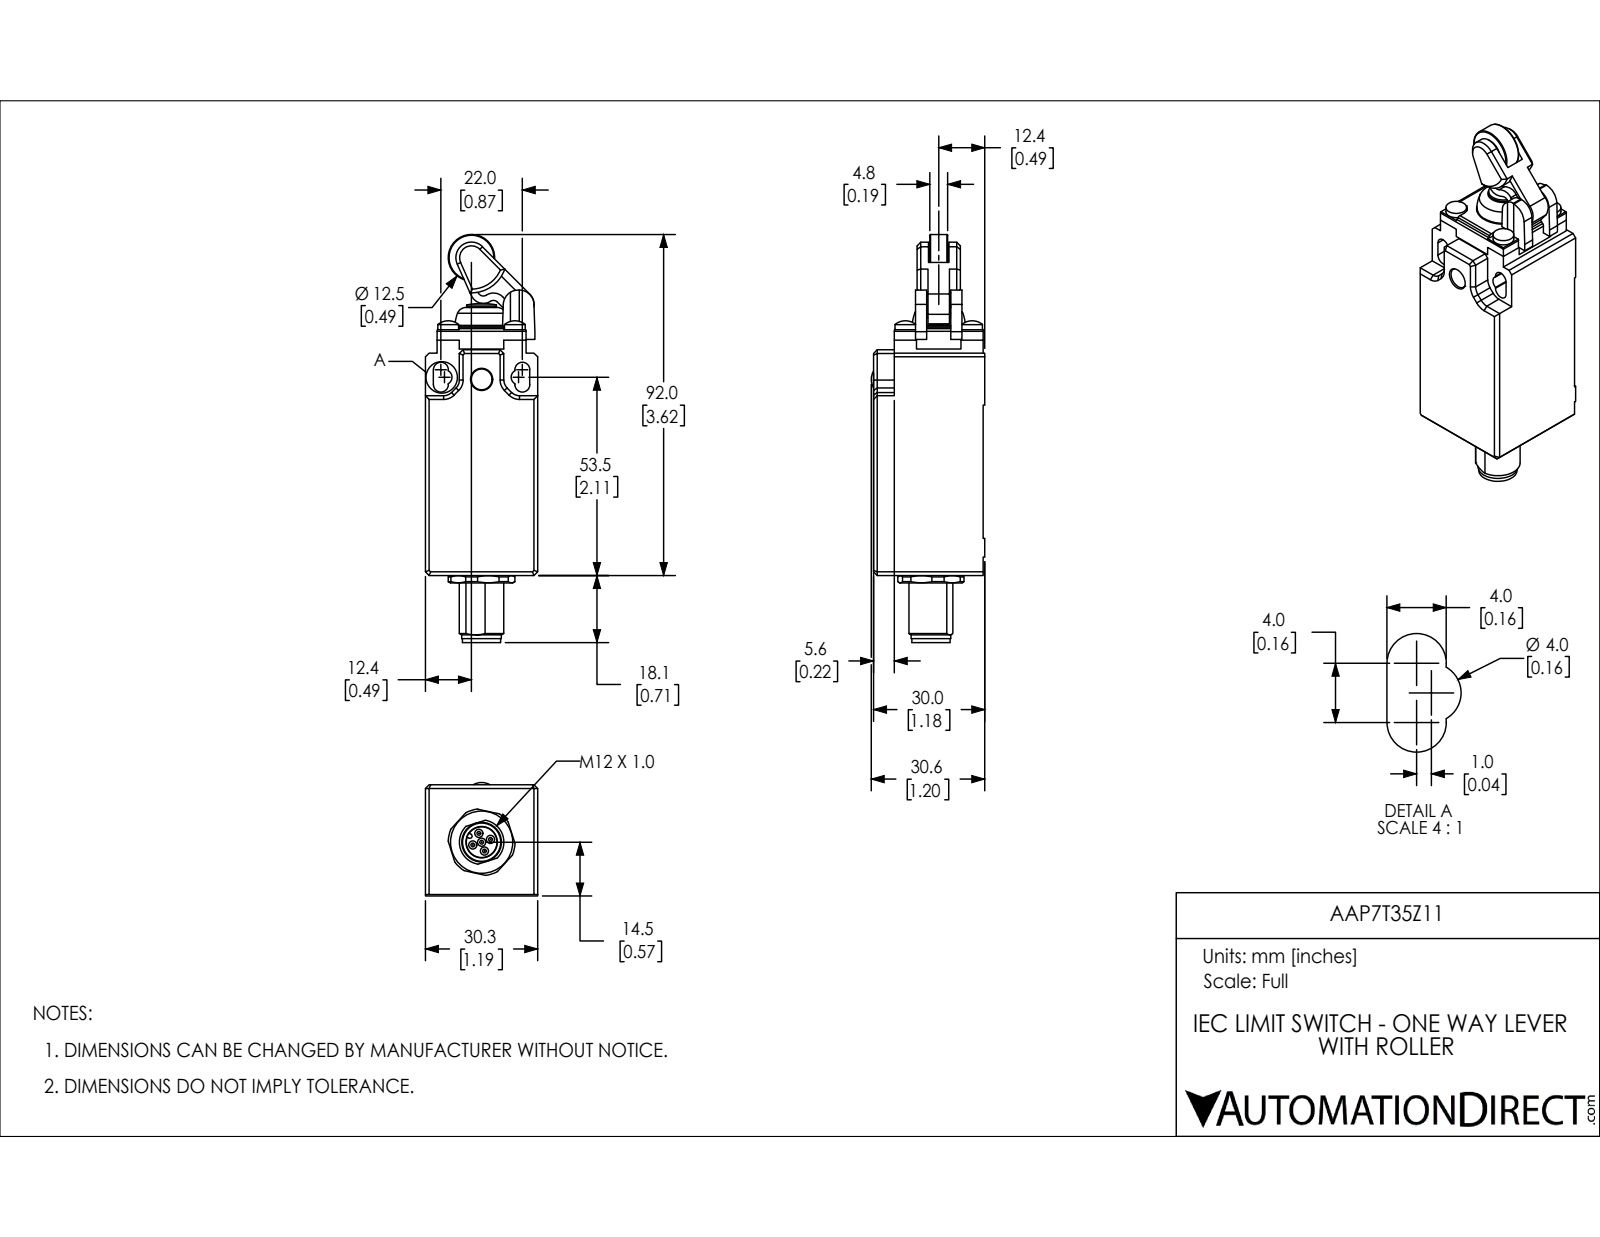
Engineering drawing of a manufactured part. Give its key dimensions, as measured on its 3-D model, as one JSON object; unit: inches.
{"part_name": "AAP7T35Z11", "step_written_by": "SolidWorks 2018 (AUTOMOTIVE_DESIGN)", "units": "inches", "bodies": {"solids": 7, "faces": 413, "planar": 186, "cylindrical": 160, "other": 67}, "overall_size": [4.334, 1.205, 1.193], "volume_in3": 3.74, "surface_area_in2": 27.69, "round_holes": [[0.087, 5], [0.236, 1], [0.319, 1], [0.512, 1], [0.551, 1], [0.571, 1], [0.63, 1]], "round_bosses_or_shafts": [[0.22, 5], [0.055, 5], [0.039, 5], [0.563, 1], [0.492, 1], [0.421, 1], [0.406, 1], [0.315, 1]], "partial_cylinders_radius": [[0.039, 8], [0.118, 8], [0.079, 6], [0.059, 2], [0.138, 2], [0.157, 2], [0.165, 2], [0.024, 1]], "face_to_face_distances": [1.193, 1.165, 2.406, 0.016, 0.236, 1.181, 0.039, 0.945, 2.61, 0.205], "hole_center_spacings": [0.098, 0.139, 0.197, 0.032, 0.083, 0.107, 0.146, 0.179]}
